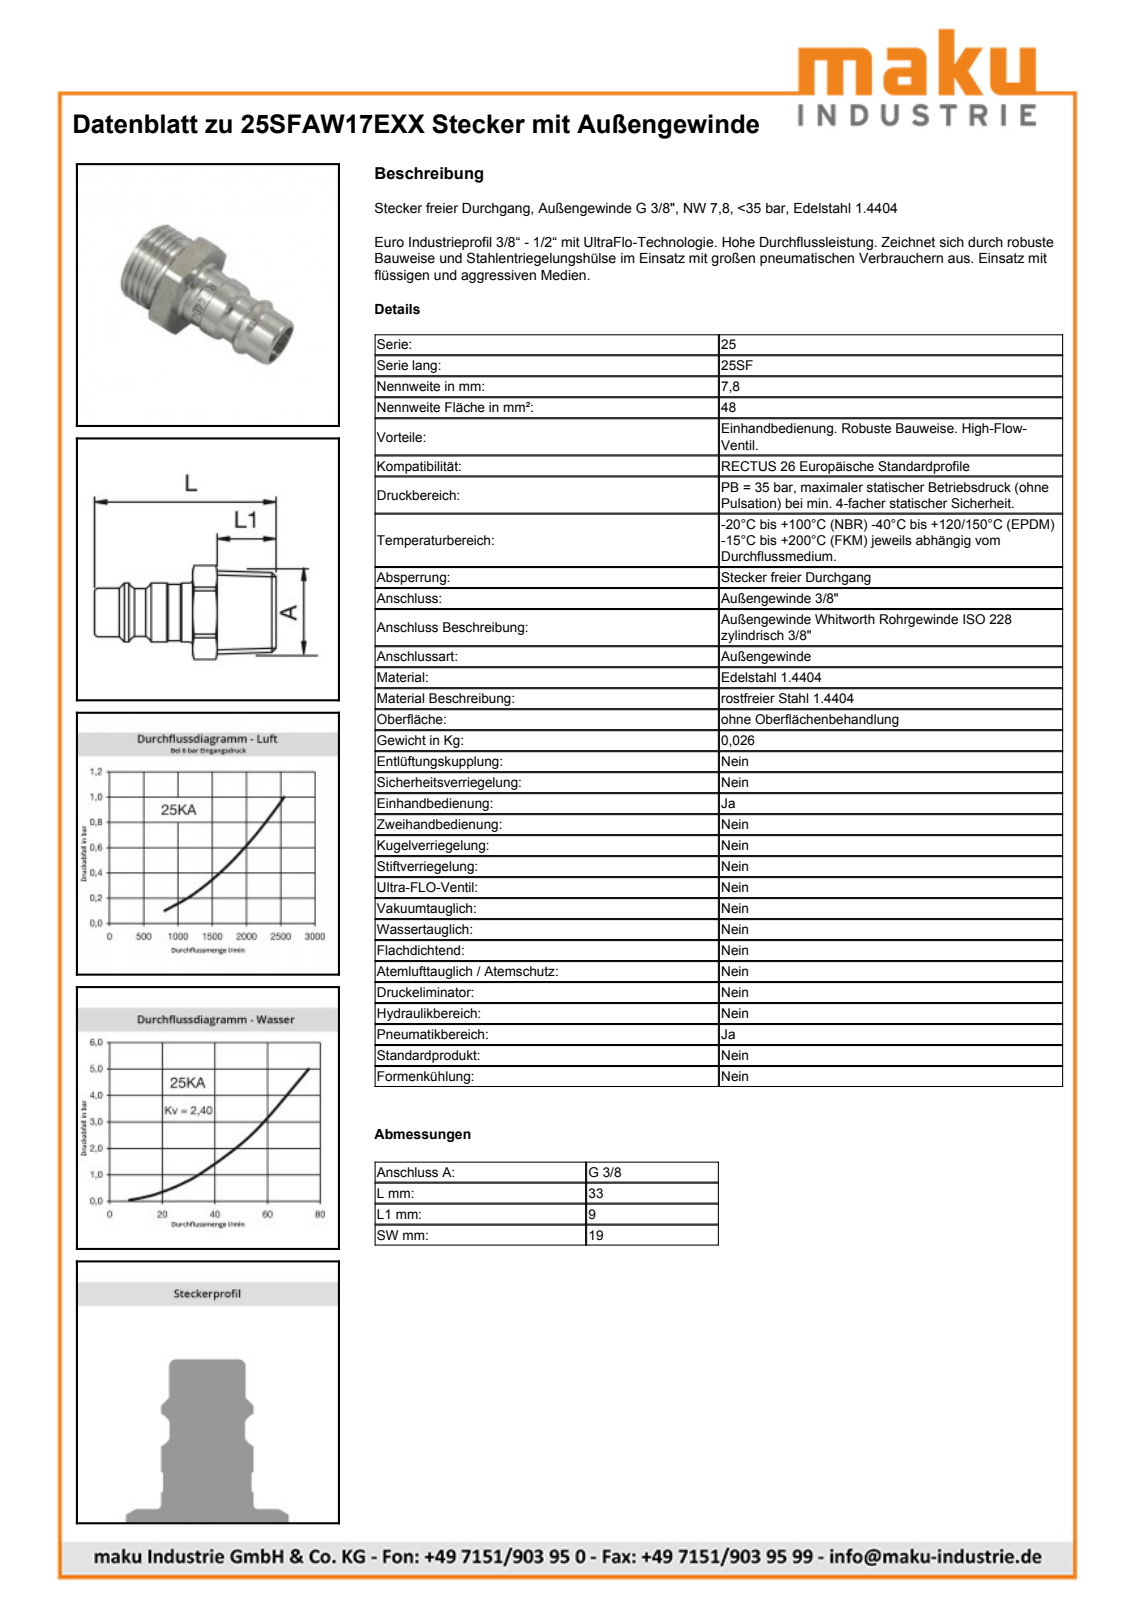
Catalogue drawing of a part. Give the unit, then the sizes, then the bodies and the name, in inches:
Units: inches
Overall size (bounding box): 1.303 × 0.843 × 0.748
Round holes (diameter × count): ⌀0.309 ×1
Round bosses / shafts (diameter × count): ⌀0.656 ×1, ⌀0.472 ×1, ⌀0.453 ×1, ⌀0.39 ×1, ⌀0.384 ×1
Partial cylindrical surfaces — rounded edges, fillets, slot ends (radius × count): R0.222 ×1, R0.421 ×1
Main face-to-face distances: 0.748, 0.161, 0.516, 0.354, 0.787, 0.949, 1.303, 0.68, 0.108, 0.269
Volume: 0.194 in³ · Surface area: 4.25 in²
Bodies: 1 solid, 230 faces (95 planar, 36 cylindrical, 99 other)
Part name (STEP PRODUCT): D106024
STEP written by: Autodesk Inventor 2011 (AUTOMOTIVE_DESIGN)
